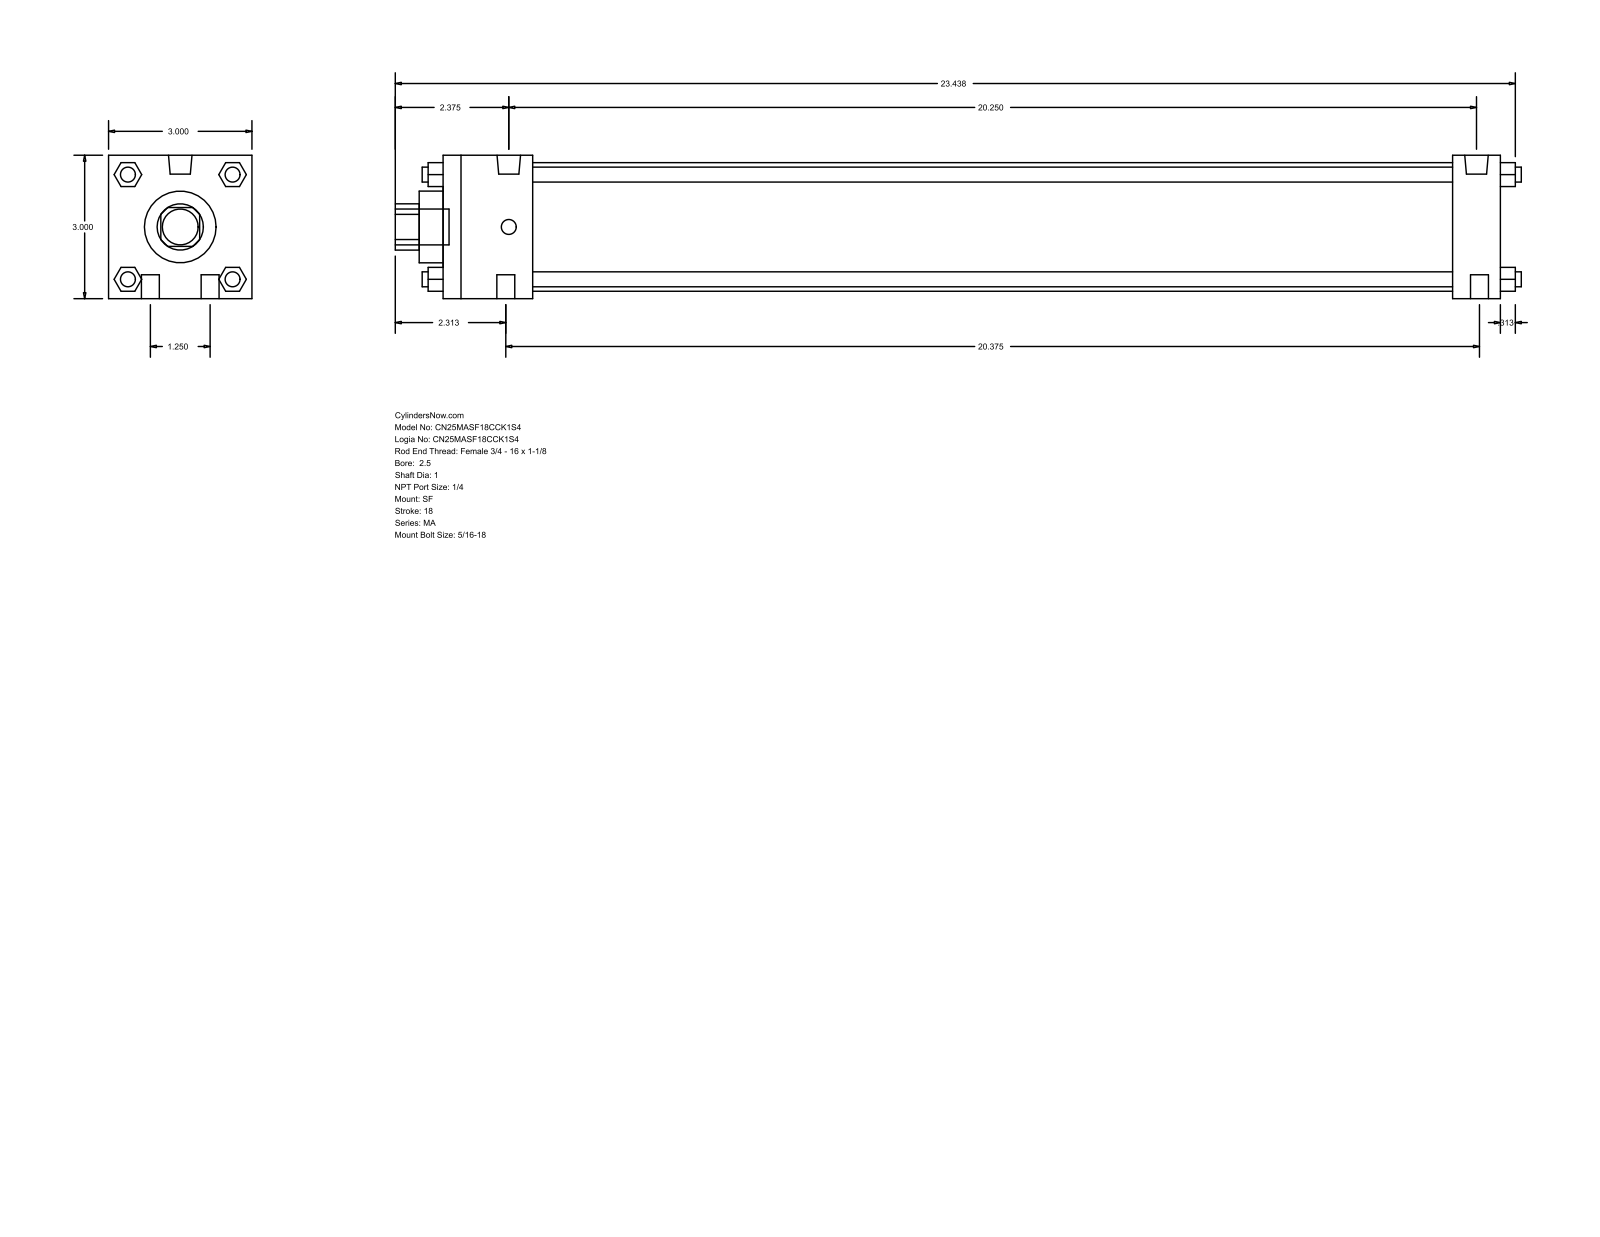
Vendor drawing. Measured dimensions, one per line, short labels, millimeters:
name: MA_SF__0250_1
written by: GSSL Pune (CONFIG_CONTROL_DESIGN)
unit: mm
bodies: 0 solids, 124 faces (94 planar, 30 cylindrical, 0 other)
size: 598.49 × 76.2 × 76.2
holes: 1× ⌀25.4, 1× ⌀38.1, 1× ⌀68.33
bosses: 6× ⌀7.94, 4× ⌀9.53, 2× ⌀12.49, 1× ⌀19.05
rounds: 1× R12.29
face distances: 76.2, 561.98, 12.7, 25.4, 536.58, 47.63, 488.95, 514.35, 27.81, 48.17
